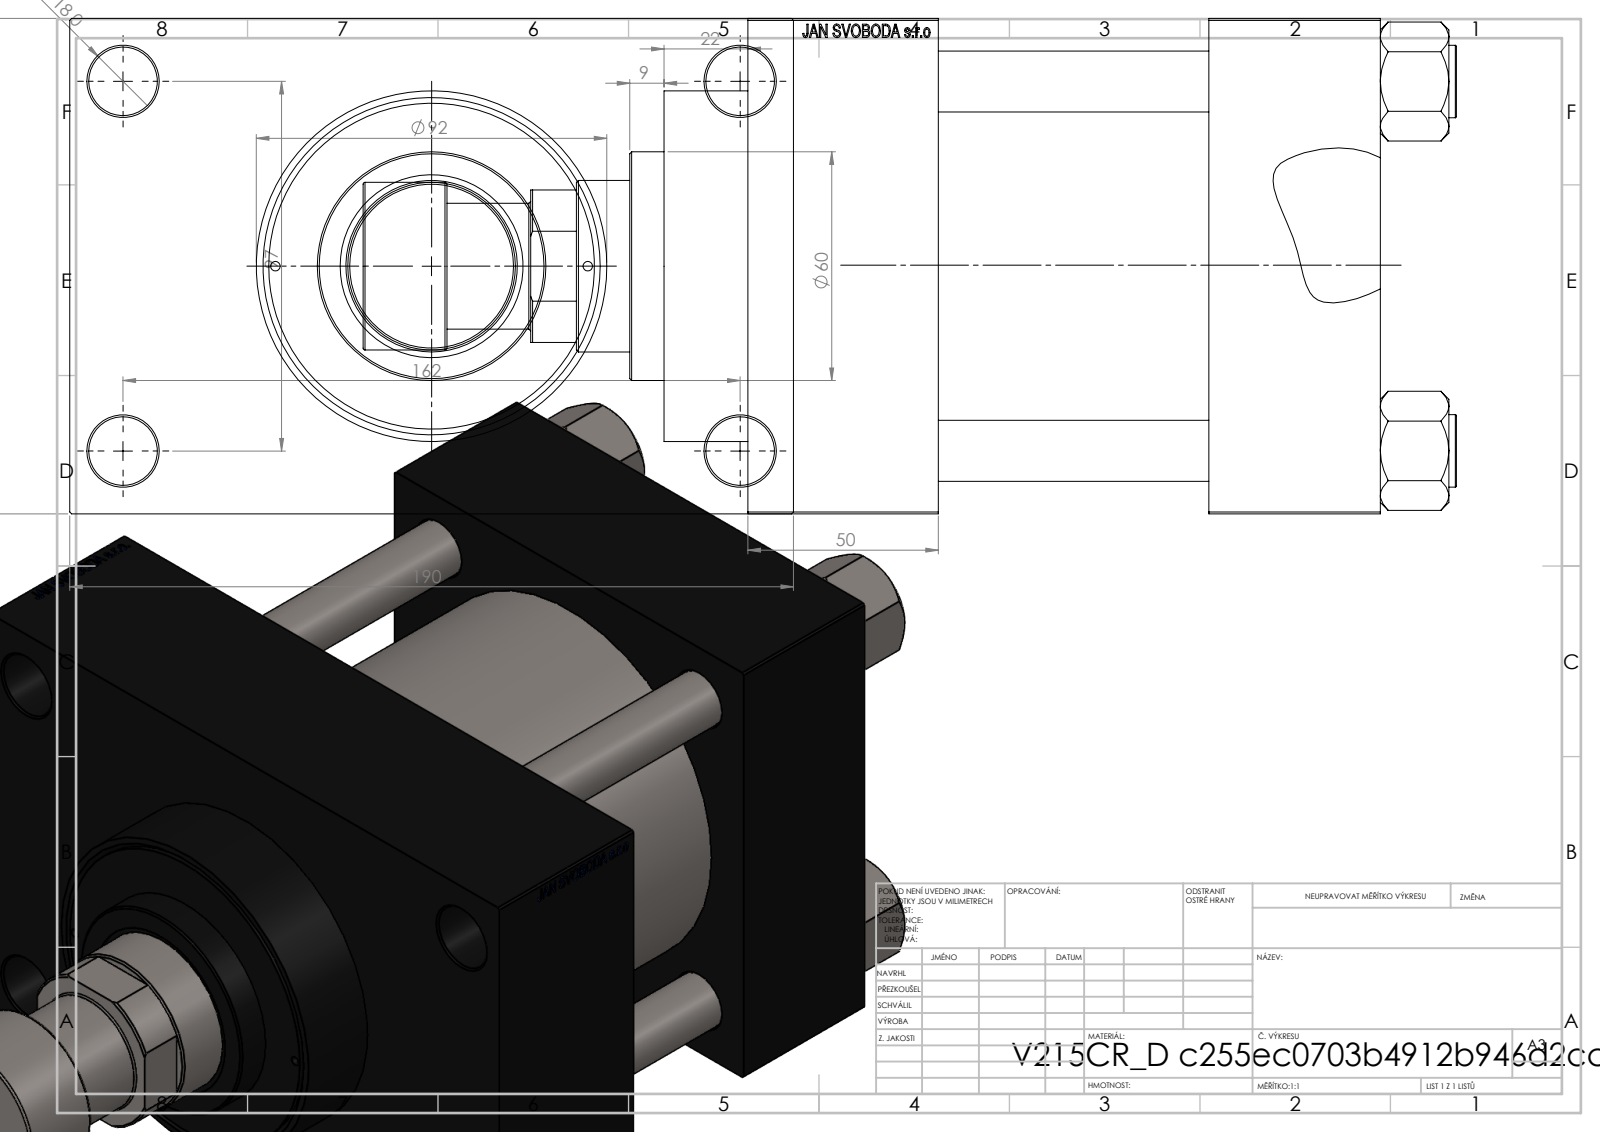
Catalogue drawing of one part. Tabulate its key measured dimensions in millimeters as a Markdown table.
| quantity | value |
| --- | --- |
| part name | V215CR_D_Body; V215_VC_A; NUT_M5_D; V215CR_ROD_END_F (+2 more) |
| STEP written by | SolidWorks 2019 (CONFIG_CONTROL_DESIGN) |
| units | millimeters |
| bodies | 12 solids, 1172 faces (550 planar, 96 cylindrical, 526 other) |
| overall size | 287 × 190 × 130 |
| volume | 2 642 000 mm³ |
| surface area | 363 101 mm² |
| round holes (diameter × count) | 16 × 4, 18 × 4, 2.5 × 2, 7 × 2, 26.44 × 2, 35 × 2, 31.5 × 1, 45 × 1, 48 × 1, 76 × 1, 85.5 × 1, 100 × 1 |
| round bosses / shafts (diameter × count) | 19 × 4, 106 × 1, 92 × 1, 60 × 1, 44 × 1, 33 × 1 |
| main face-to-face distances | 130, 116, 45, 71, 166, 121, 50, 30, 160, 70 |
| hole center spacings | 32.55, 49.02, 62.87, 68.52, 94.41, 96.9, 101.73, 102.27 |
